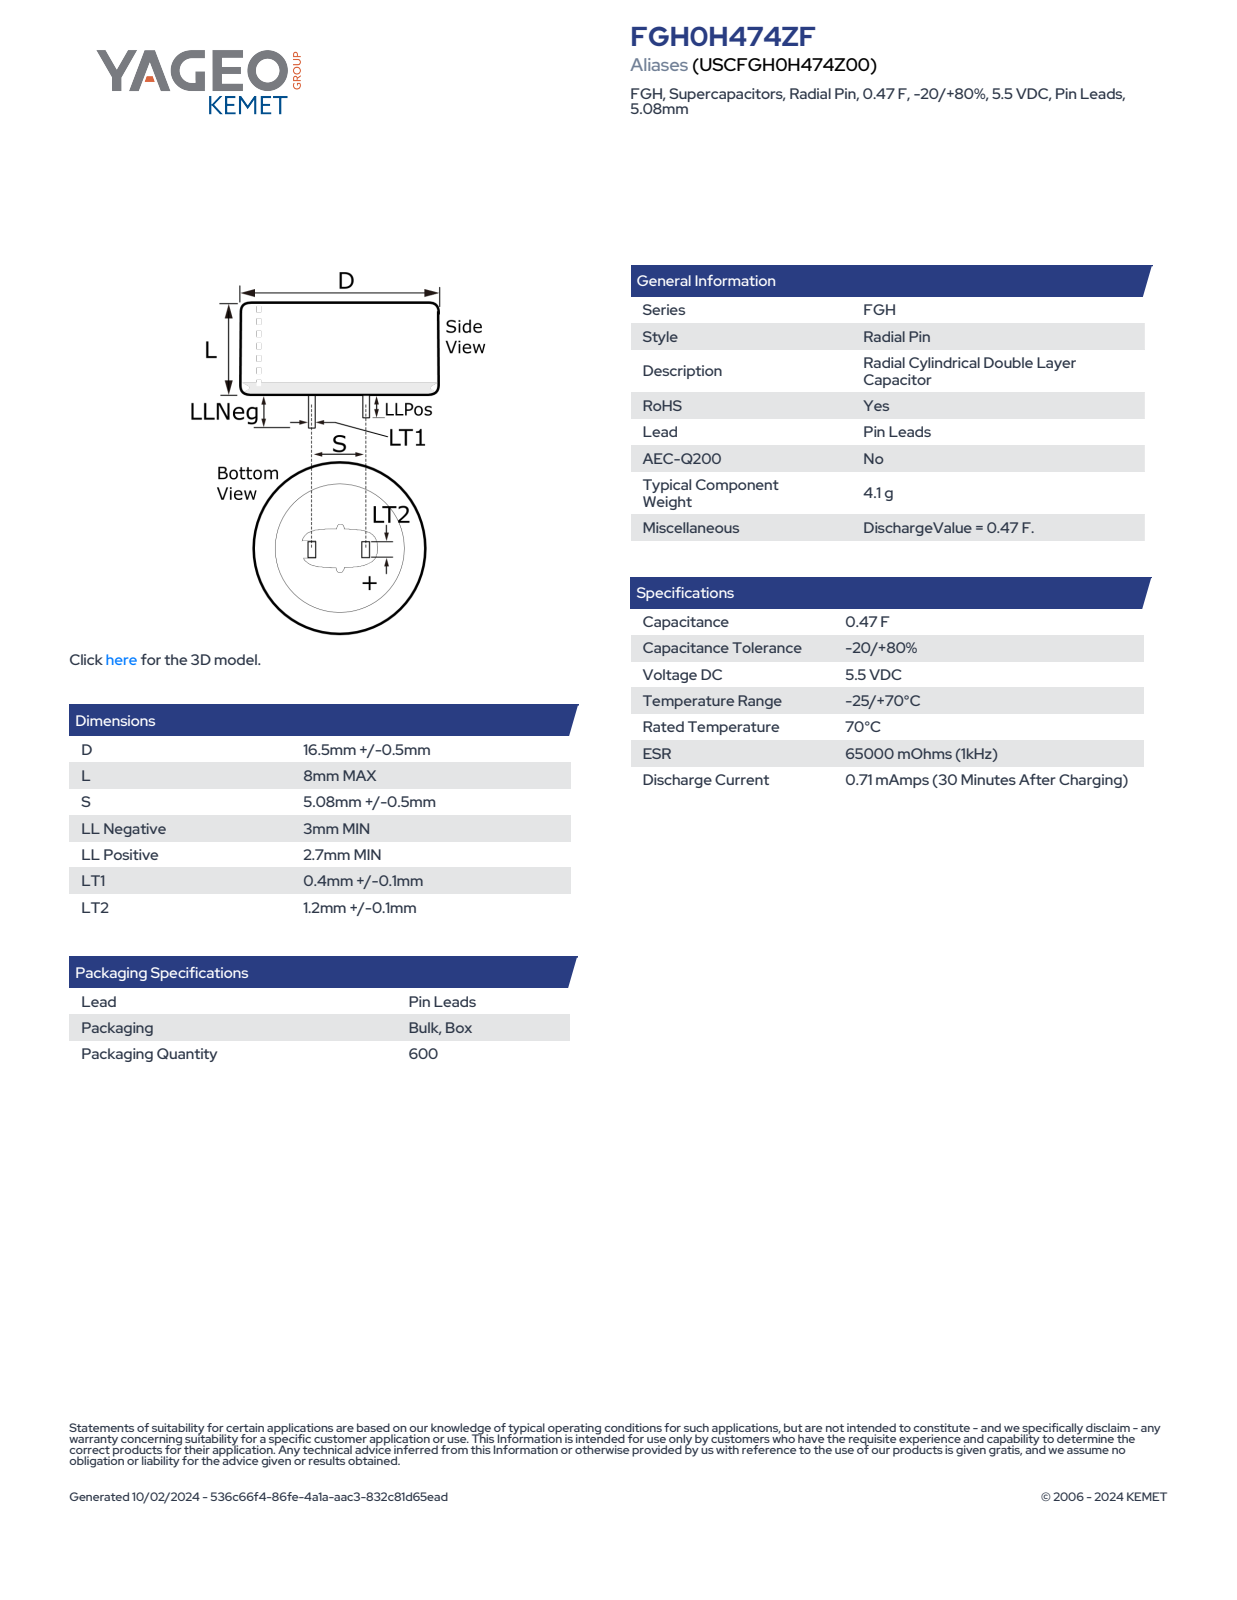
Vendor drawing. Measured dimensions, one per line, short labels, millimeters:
name: CDR_LPLLN_D17L8S5.08LLNEG3LLPOS2.7LT10.5LT21.3
written by: SolidWorks 2014 (AUTOMOTIVE_DESIGN)
unit: mm
bodies: 1 solid, 78 faces (70 planar, 4 cylindrical, 4 other)
size: 17 × 17 × 11
volume: 1 814 mm³; area: 878 mm²
bosses: 1× ⌀17
rounds: 1× R8.51
face distances: 8, 0.5, 5.08, 5.58, 4.58, 1.3, 3, 11, 2.7, 10.7
